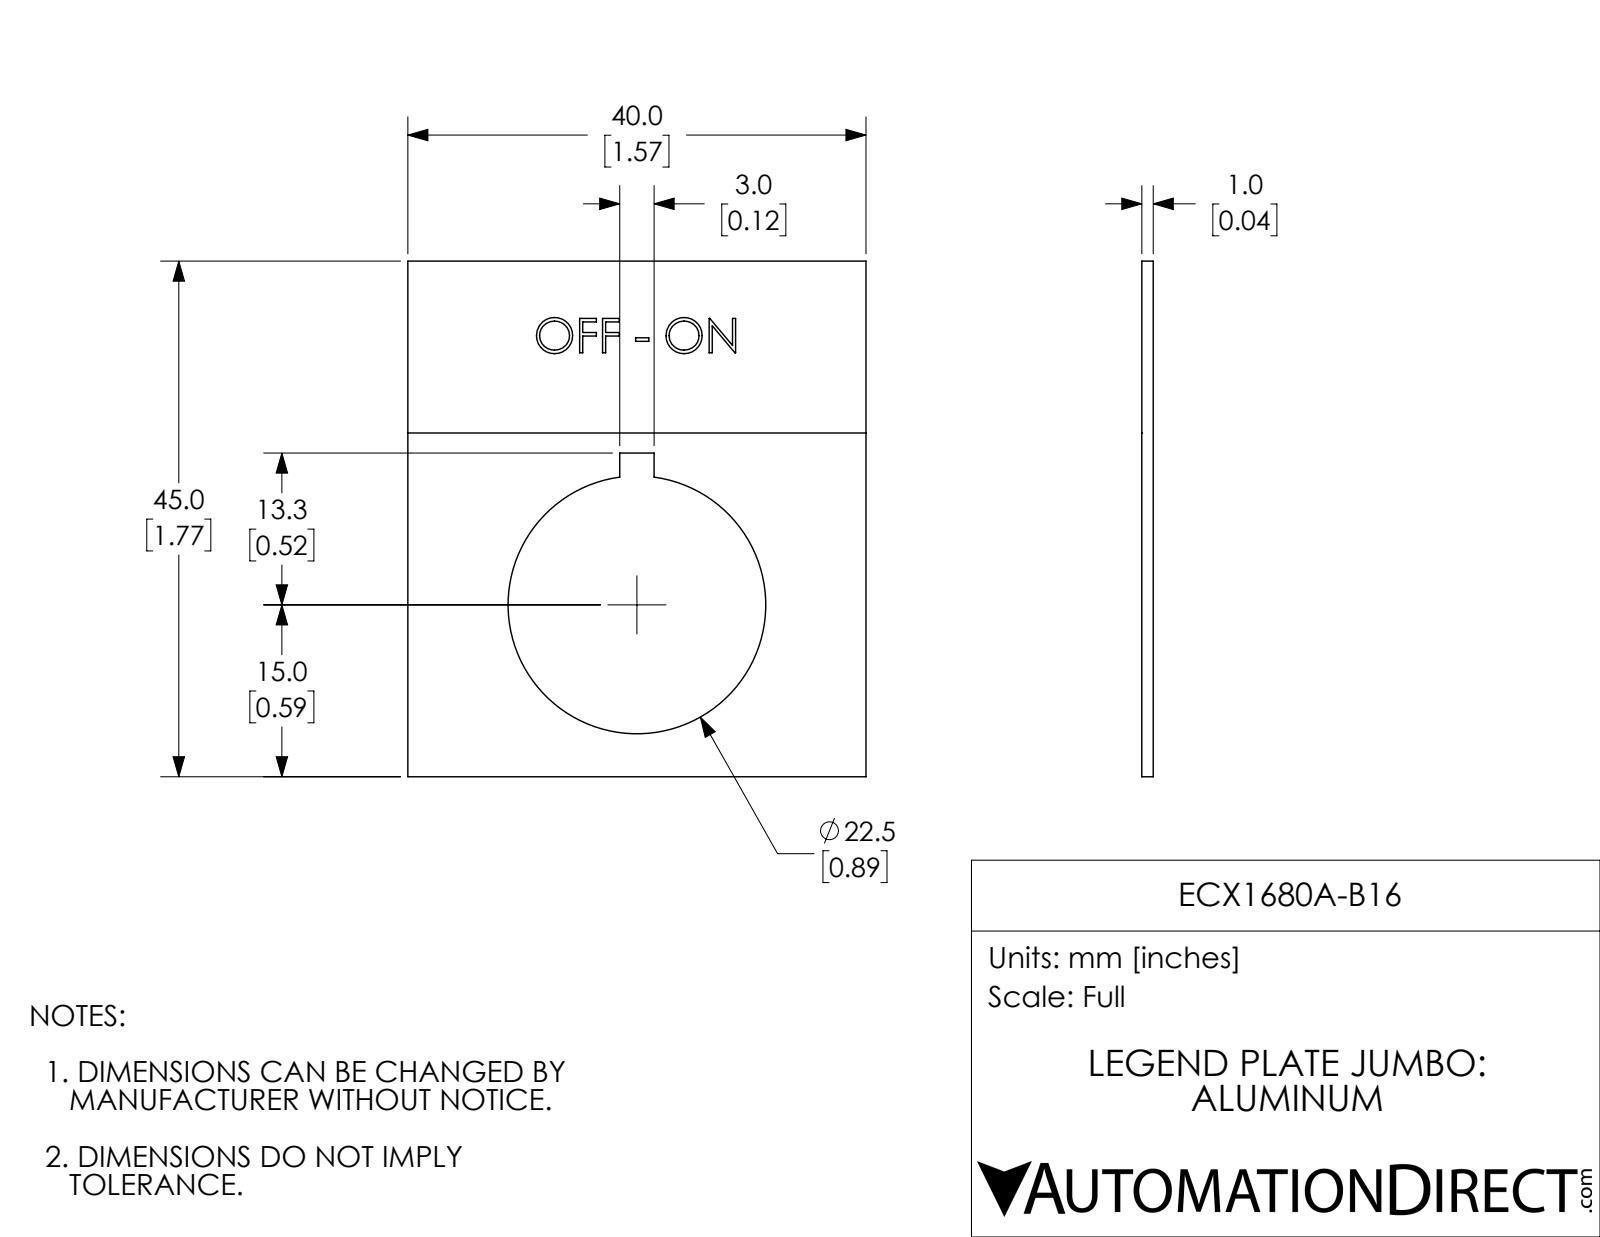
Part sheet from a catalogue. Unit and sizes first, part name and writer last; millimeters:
Units: millimetres
Overall size (bounding box): 45 × 40 × 1
Round holes (diameter × count): ⌀22.5 ×1
Main face-to-face distances: 1, 0.99, 40, 45, 18.5, 21.5, 28.25, 16.75, 3, 15
Volume: 1 393 mm³ · Surface area: 3 038 mm²
Bodies: 1 solid, 72 faces (53 planar, 3 cylindrical, 16 other)
Part name (STEP PRODUCT): ECX1680A-B16
STEP written by: SolidWorks 2017 (AUTOMOTIVE_DESIGN)
